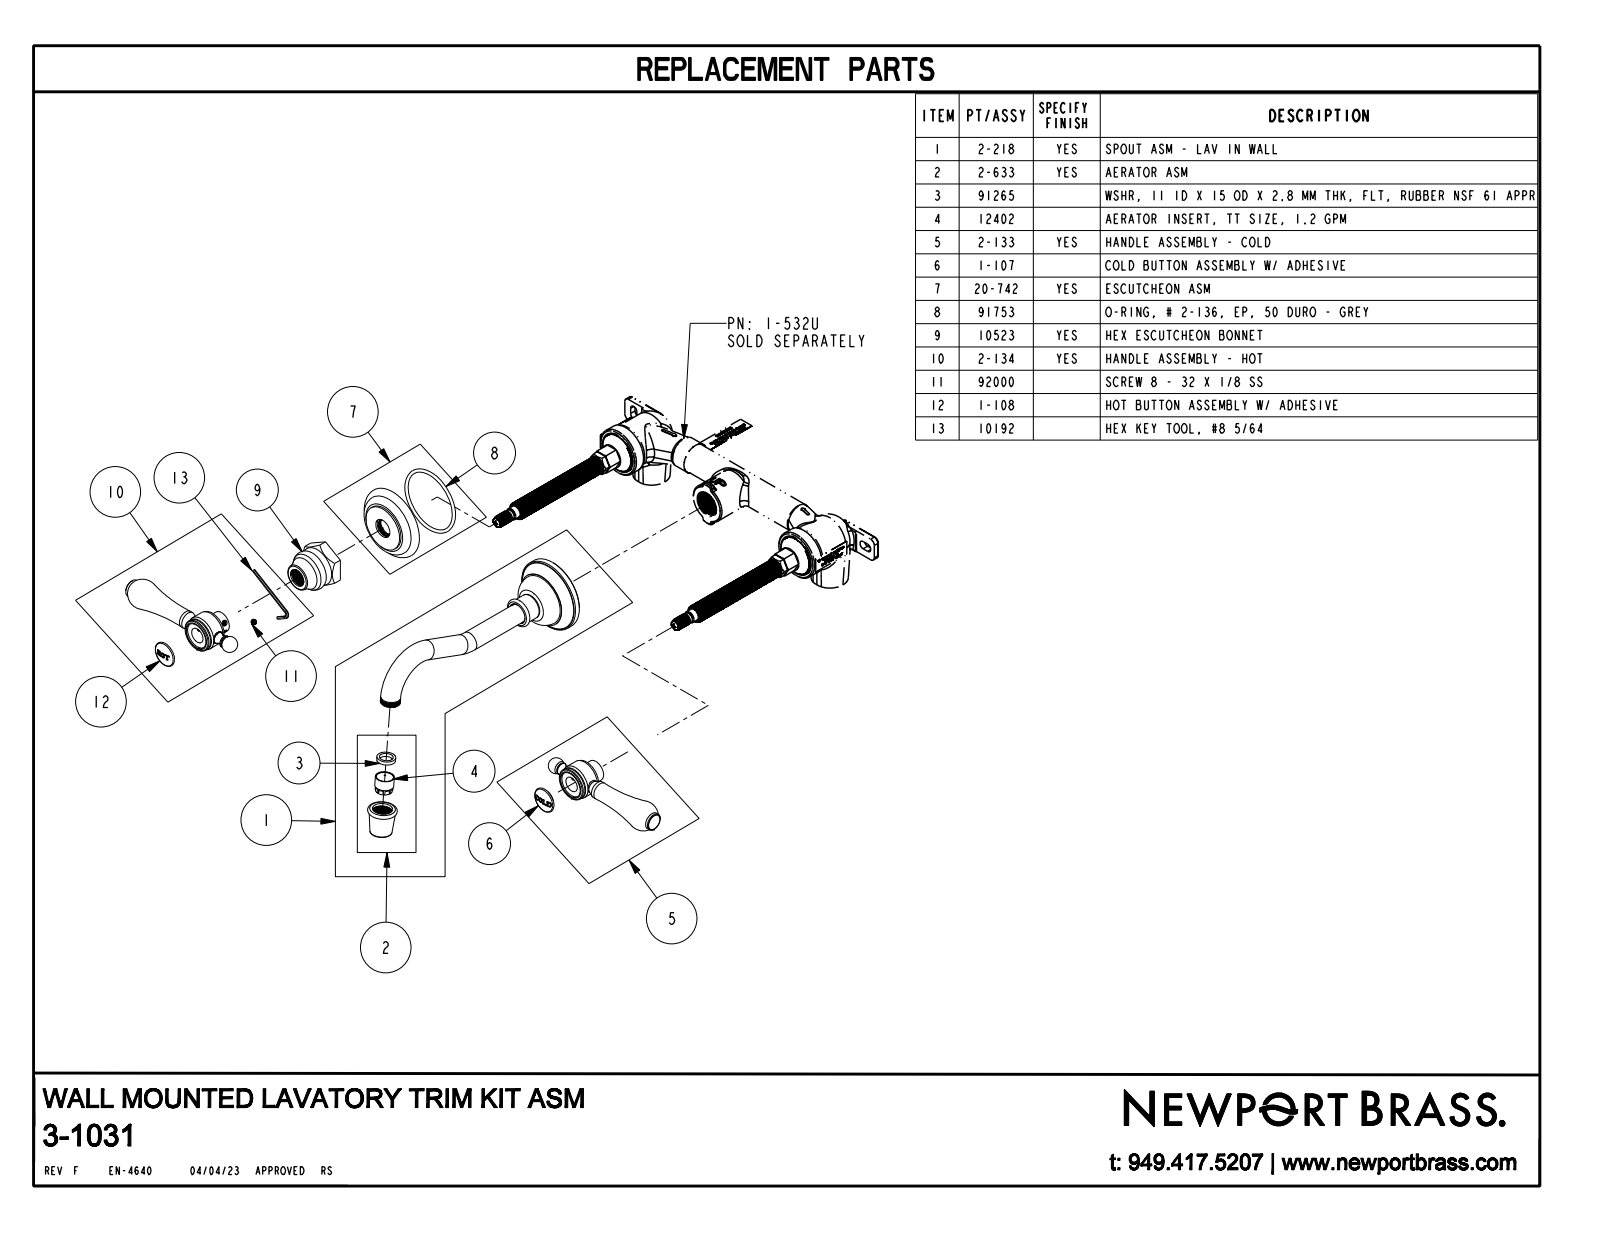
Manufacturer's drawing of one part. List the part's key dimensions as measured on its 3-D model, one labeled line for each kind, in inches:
Part name (STEP PRODUCT): 3-1031_SW0001
STEP written by: CREO PARAMETRIC BY PTC INC, 2018400 (AUTOMOTIVE_DESIGN)
Units: inches
Bodies: 3 solids, 369 faces (127 planar, 90 cylindrical, 152 other)
Overall size (bounding box): 14.619 × 7.663 × 2.445
Volume: 14.86 in³ · Surface area: 81.62 in²
Round holes (diameter × count): ⌀0.41 ×1
Round bosses / shafts (diameter × count): ⌀1.482 ×2, ⌀1.115 ×2, ⌀1.055 ×2, ⌀0.687 ×2, ⌀0.625 ×2, ⌀2.36 ×1, ⌀1.764 ×1, ⌀0.814 ×1
Partial cylindrical surfaces — rounded edges, fillets, slot ends (radius × count): R0.006 ×7, R0.024 ×7, R0.03 ×5, R0.048 ×3, R0.018 ×2, R0.036 ×2, R0.041 ×2, R0.054 ×1
Main face-to-face distances: 1.313, 3.937, 0.375, 0.96, 0.585, 7.874, 1.313, 5.25, 2.624, 0.437
